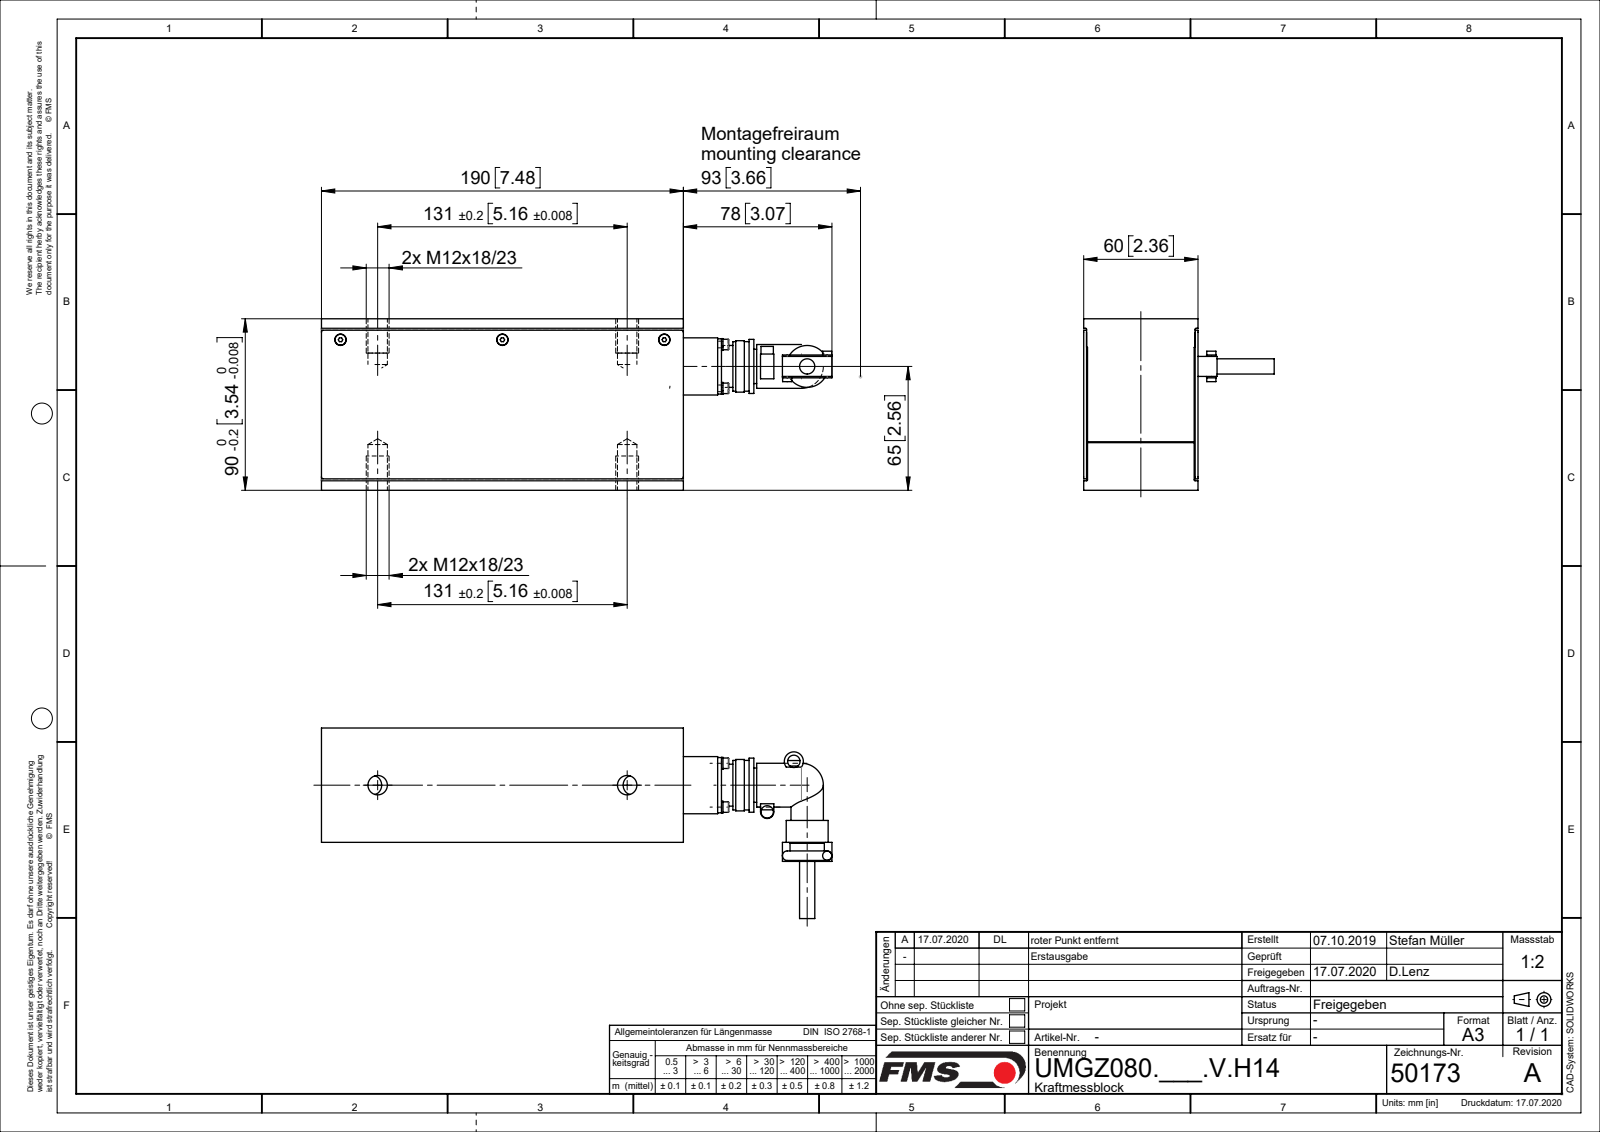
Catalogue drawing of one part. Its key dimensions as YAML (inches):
part_name: "U50173; U4957704; U49541; L49026 (+6 more)"
step_written_by: "Mechanical Desktop 2007 (CONFIG_CONTROL_DESIGN)"
units: inches
bodies: {solids: 19, faces: 399, planar: 156, cylindrical: 160, other: 83}
overall_size: [10.551, 3.937, 3.543]
volume: 63.65
surface_area: 236
round_holes:
  - {diameter: 0.102, count: 7}
  - {diameter: 0.126, count: 4}
  - {diameter: 0.134, count: 4}
  - {diameter: 0.138, count: 4}
  - {diameter: 0.236, count: 3}
  - {diameter: 0.42, count: 2}
  - {diameter: 0.43, count: 1}
  - {diameter: 0.906, count: 1}
round_bosses_or_shafts:
  - {diameter: 0.118, count: 7}
  - {diameter: 0.244, count: 4}
  - {diameter: 0.217, count: 4}
  - {diameter: 0.866, count: 2}
  - {diameter: 0.256, count: 2}
  - {diameter: 0.189, count: 2}
  - {diameter: 1.118, count: 1}
  - {diameter: 1.063, count: 1}
partial_cylinders:
  - {radius: 0.039, count: 4}
  - {radius: 0.098, count: 2}
  - {radius: 0.138, count: 1}
  - {radius: 0.197, count: 1}
face_to_face_distances: [2.303, 0.059, 0.079, 0.02, 2.283, 2.224, 2.362, 2.244, 2.205, 3.543]
hole_center_spacings: [0.64, 0.906, 1.281, 3.346, 5.157, 6.693]
